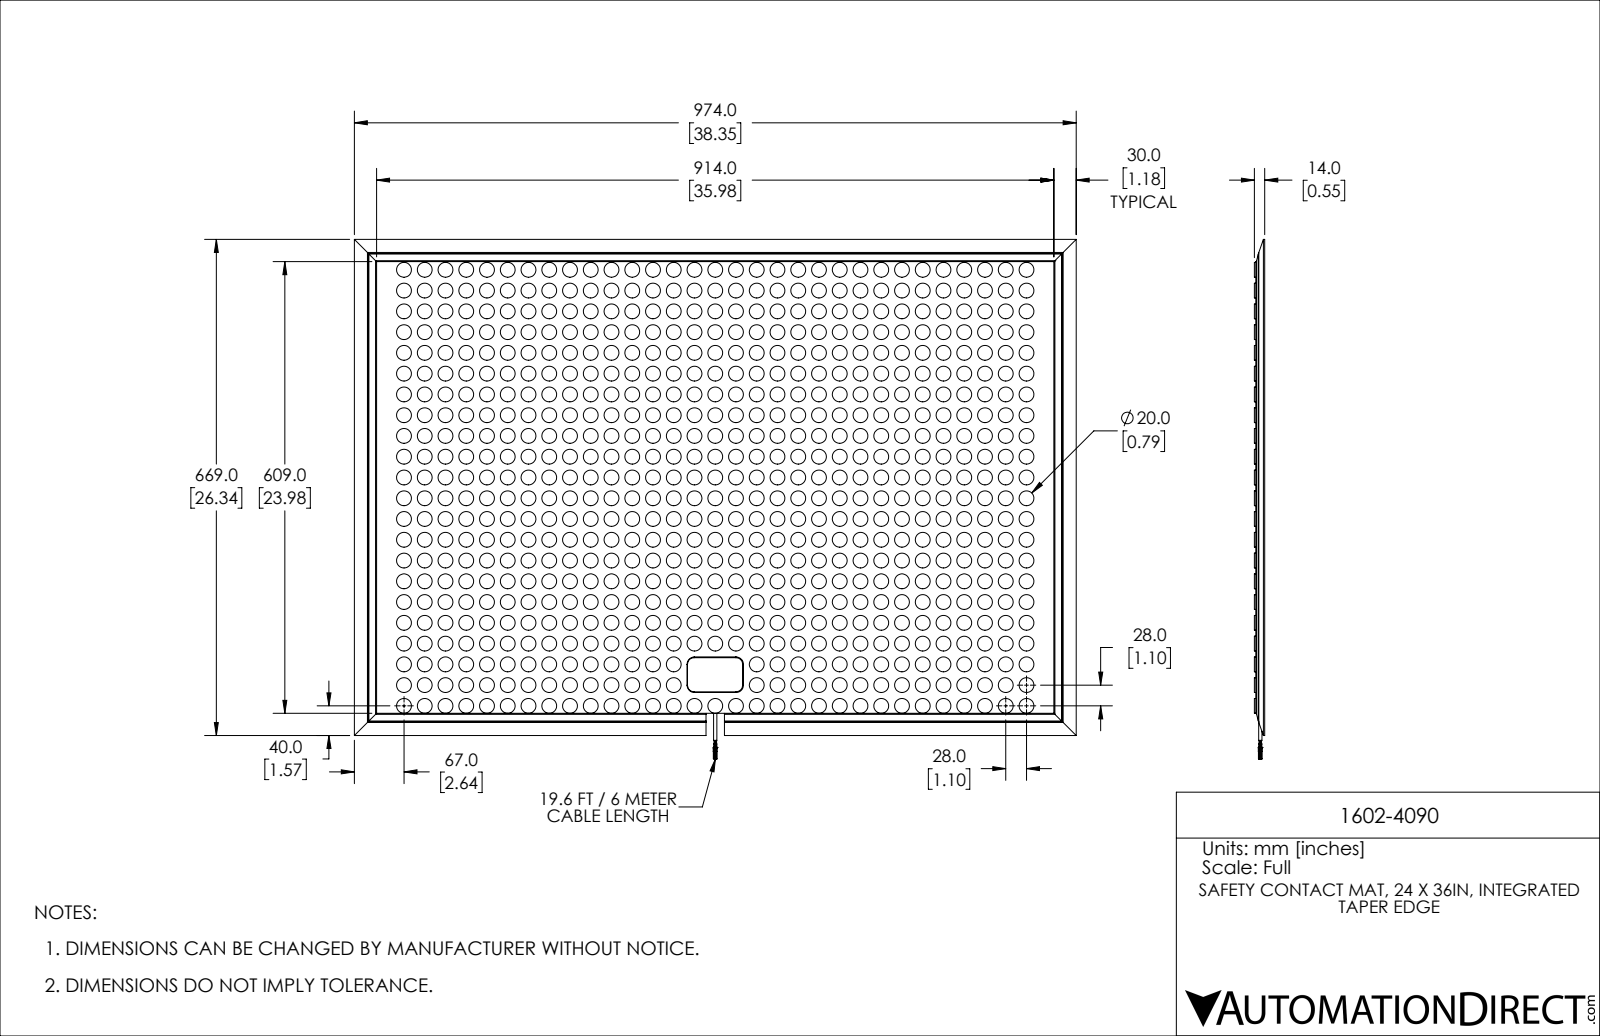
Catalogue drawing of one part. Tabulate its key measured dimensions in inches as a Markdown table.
| quantity | value |
| --- | --- |
| part name | CAD-17.05757; CAD-20.00252; CAD-16.00097_einfache Darstellung; CAD-17.05386_einfache Darstellung (+2 more) |
| STEP written by | SolidWorks 2019 (AUTOMOTIVE_DESIGN) |
| units | inches |
| bodies | 681 solids, 2905 faces (1430 planar, 1434 cylindrical, 41 other) |
| overall size | 38.346 × 27.579 × 0.551 |
| volume | 466 in³ |
| surface area | 2 962 in² |
| round bosses / shafts (diameter × count) | 0.787 × 676, 0.047 × 20, 0.031 × 8, 0.173 × 1 |
| partial cylindrical surfaces (radius × count) | 0.394 × 6, 0.039 × 4 |
| main face-to-face distances | 0.472, 0.079, 0.551, 23.976, 35.984, 0.134, 0.055, 0.417, 0.413, 0.138 |
